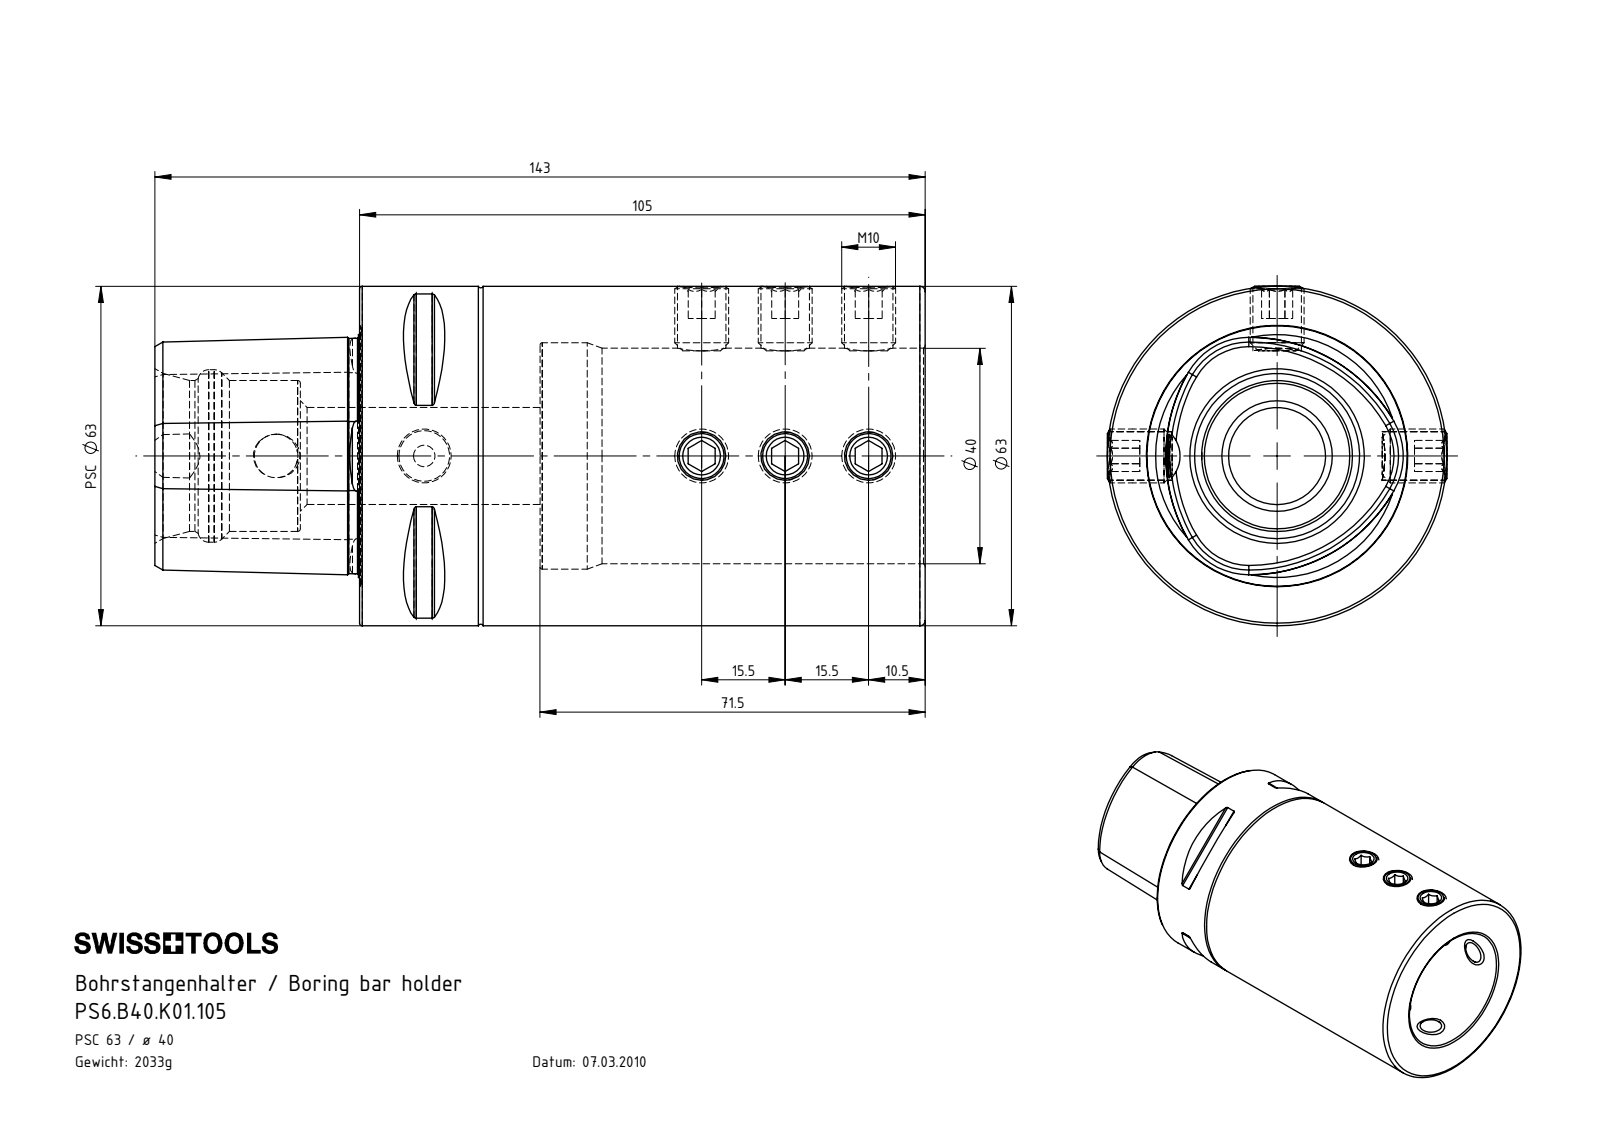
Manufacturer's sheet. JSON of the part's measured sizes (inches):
{"part_name": "ISO 4026 - M10 x 12_PreviewCfg; PS6-B40.K01.105_B; PS6.B40.K01.105", "step_written_by": "SolidWorks 2017 (AUTOMOTIVE_DESIGN)", "units": "inches", "bodies": {"solids": 10, "faces": 303, "planar": 101, "cylindrical": 67, "other": 135}, "overall_size": [5.63, 2.48, 2.48], "volume_in3": 15.83, "surface_area_in2": 82.27, "round_holes": [[0.354, 6], [0.157, 1], [0.319, 1], [0.709, 1], [1.102, 1], [1.26, 1], [1.575, 1], [1.654, 1]], "round_bosses_or_shafts": [[0.394, 6], [2.48, 1]], "partial_cylinders_radius": [[0.02, 8], [0.236, 1]], "face_to_face_distances": [2.815, 4.134, 1.319, 1.496, 5.63, 0.197, 0.61, 0.305, 0.236, 0.98], "hole_center_spacings": [0.61, 1.22, 1.083, 2.028, 2.638, 3.11, 3.248, 3.72]}
